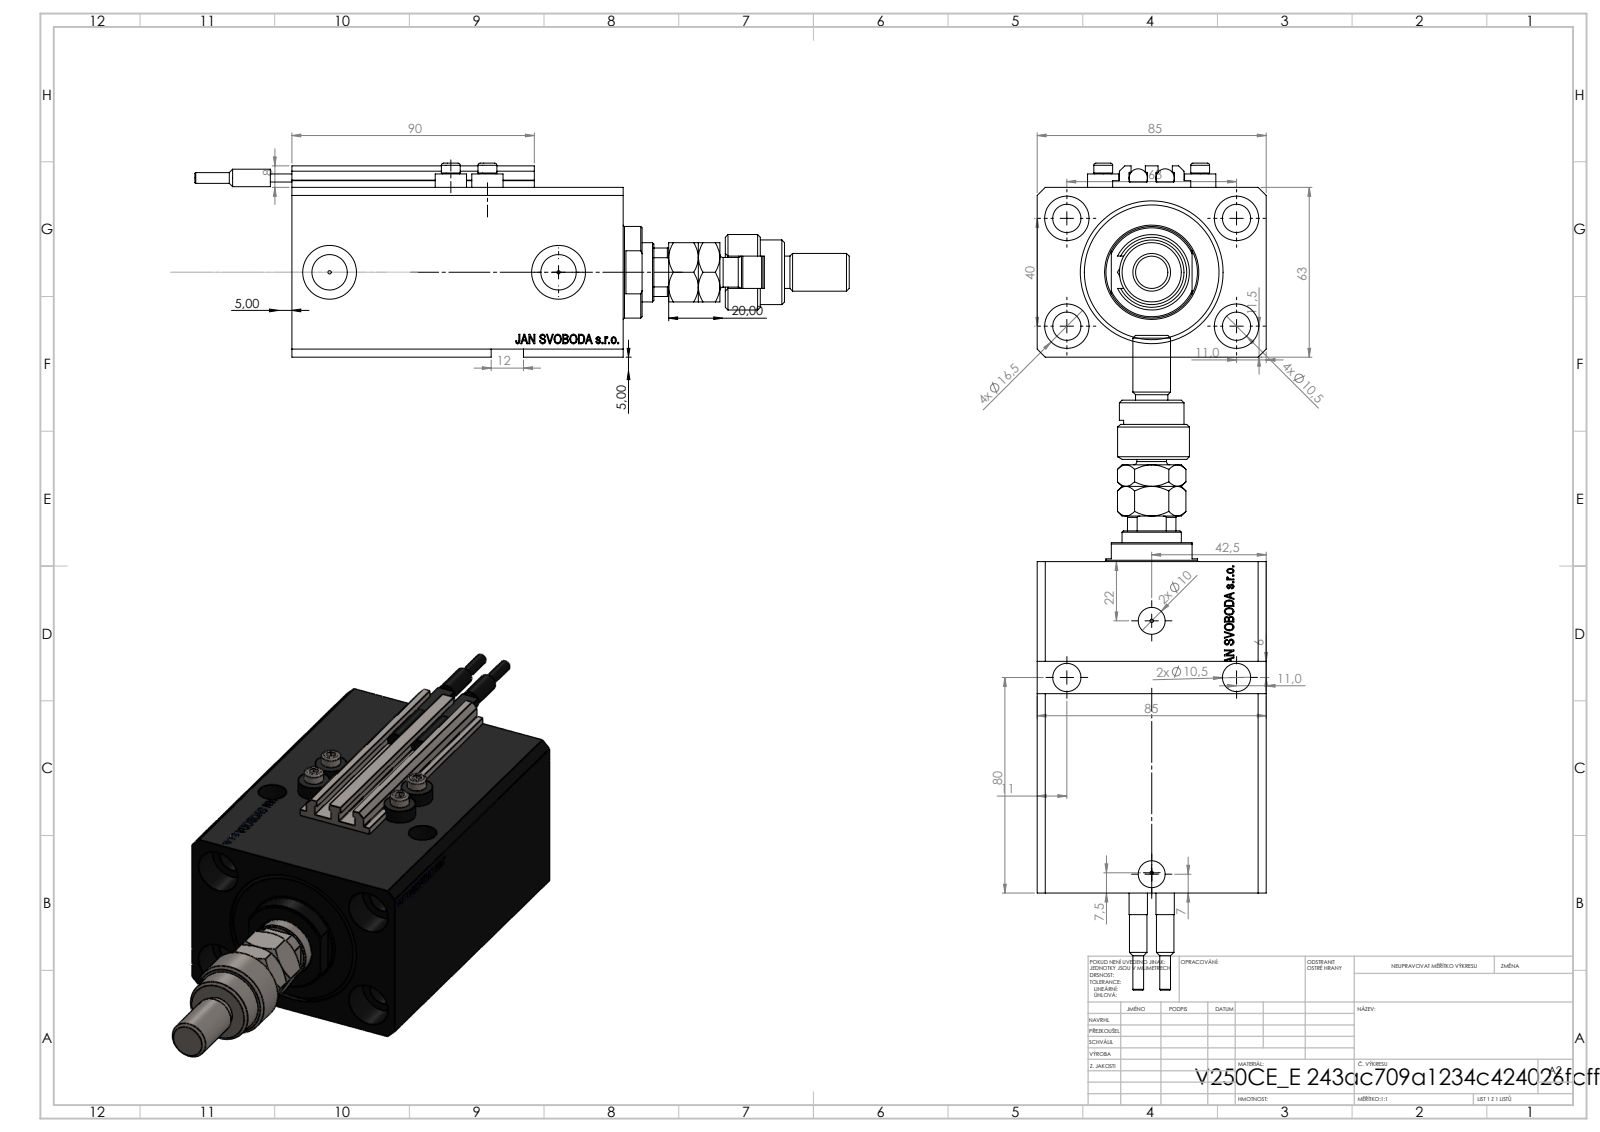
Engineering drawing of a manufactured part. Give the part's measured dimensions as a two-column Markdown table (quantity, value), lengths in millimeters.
| quantity | value |
| --- | --- |
| part name | FEMALE_PART_FOR_DFA; V250CE_C_VCP; SWITCH_V250CE; ALLEN BOLT V250CE (+3 more) |
| STEP written by | SolidWorks 2019 (CONFIG_CONTROL_DESIGN) |
| units | millimeters |
| bodies | 12 solids, 1244 faces (595 planar, 171 cylindrical, 478 other) |
| overall size | 243 × 85 × 72 |
| volume | 582 126 mm³ |
| surface area | 130 039 mm² |
| round holes (diameter × count) | 10.5 × 8, 1.25 × 4, 4 × 4, 16.5 × 4, 10 × 2, 13.16 × 2, 20 × 2, 12.5 × 1, 22 × 1, 40 × 1, 53 × 1 |
| round bosses / shafts (diameter × count) | 11.6 × 4, 7 × 4, 6.8 × 2, 6.5 × 2, 4 × 2, 34 × 1, 28 × 1, 24 × 1 |
| partial cylindrical surfaces (radius × count) | 0.2 × 10, 9.75 × 1, 10.5 × 1 |
| main face-to-face distances | 63, 85, 17, 123, 106, 3, 11.4, 94.6, 111.6, 65 |
| hole center spacings | 37.31, 63, 13.6, 15.4, 24.96, 27.54, 33.62, 36 |
